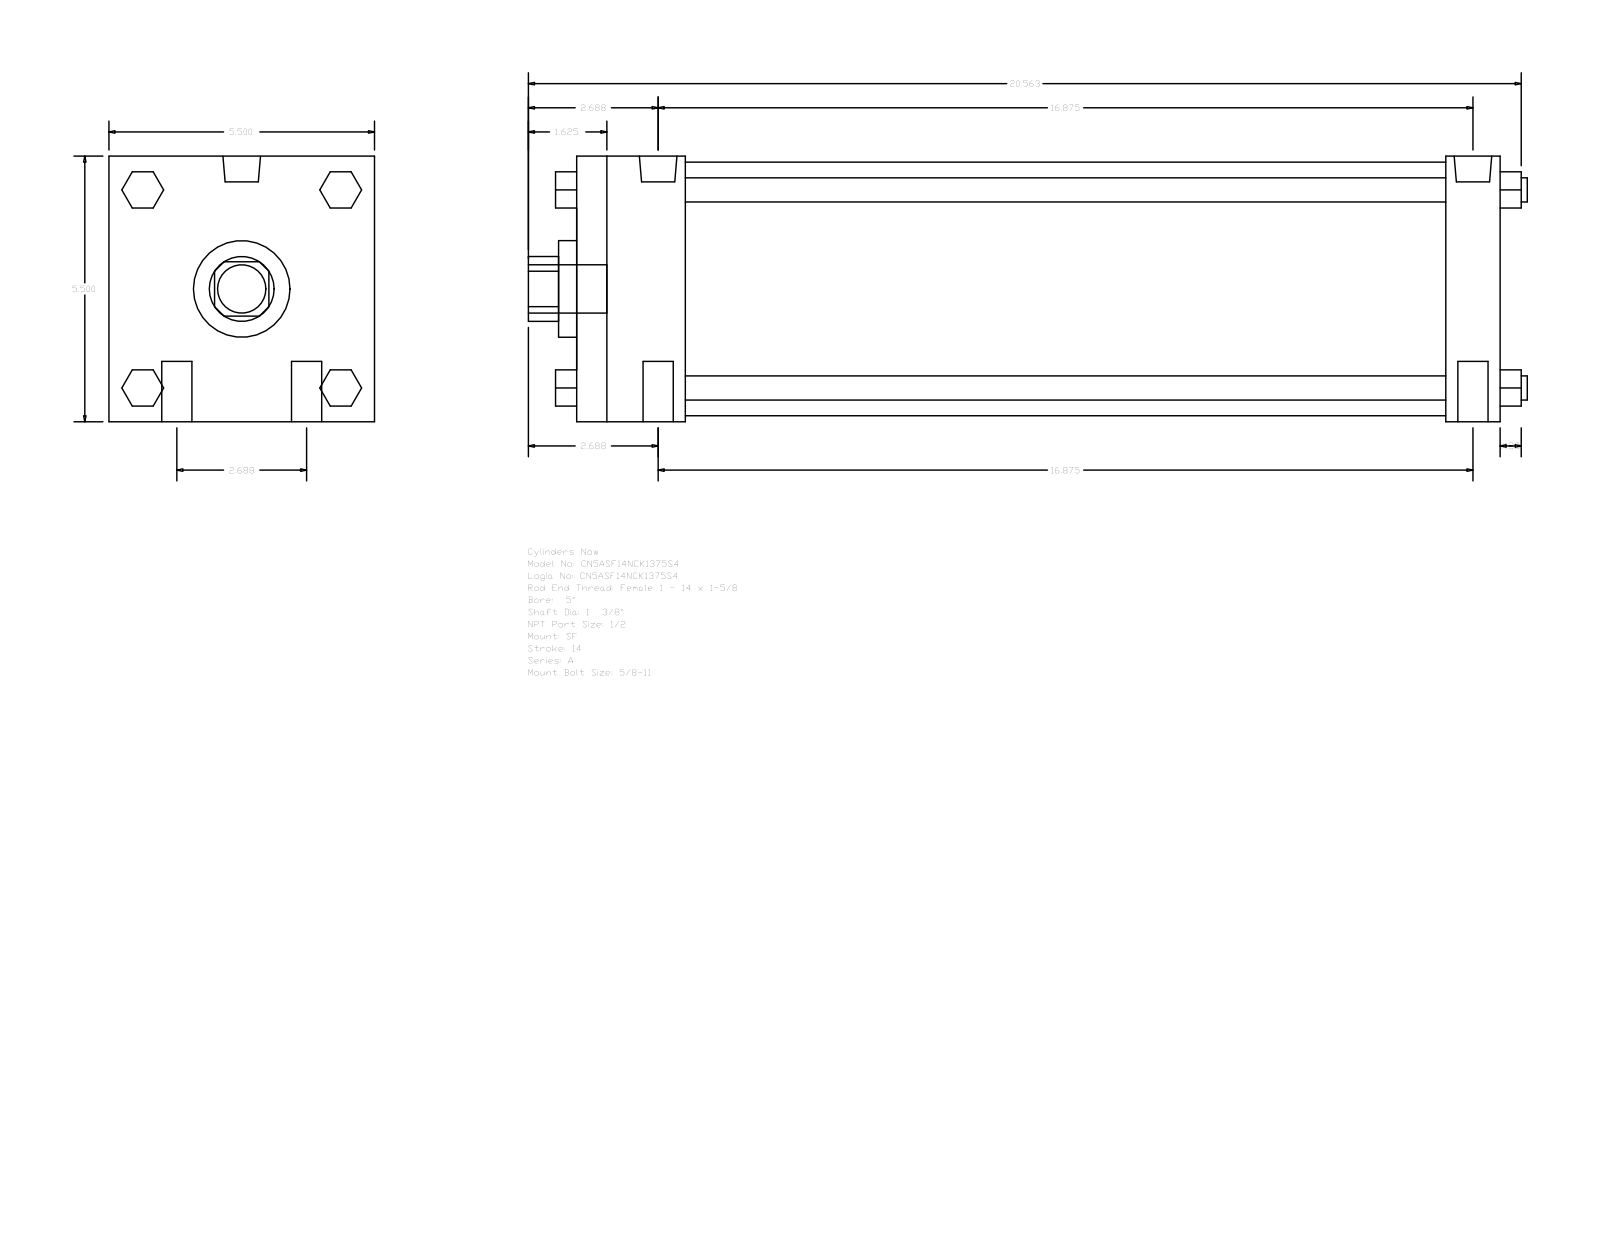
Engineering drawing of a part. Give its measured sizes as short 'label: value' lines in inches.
name: A_SF__0500_1.375
written by: GSSL Pune (CONFIG_CONTROL_DESIGN)
unit: in
bodies: 0 solids, 124 faces (94 planar, 30 cylindrical, 0 other)
size: 20.687 × 5.5 × 5.5
holes: 1× ⌀1.375, 1× ⌀2, 1× ⌀5.25
bosses: 4× ⌀0.625, 4× ⌀0.5, 2× ⌀0.778, 2× ⌀0.344, 1× ⌀1
rounds: 1× R0.672
face distances: 5.5, 19.125, 1.125, 2.25, 18, 15.75, 16.875, 0.75, 2.05, 3.55
